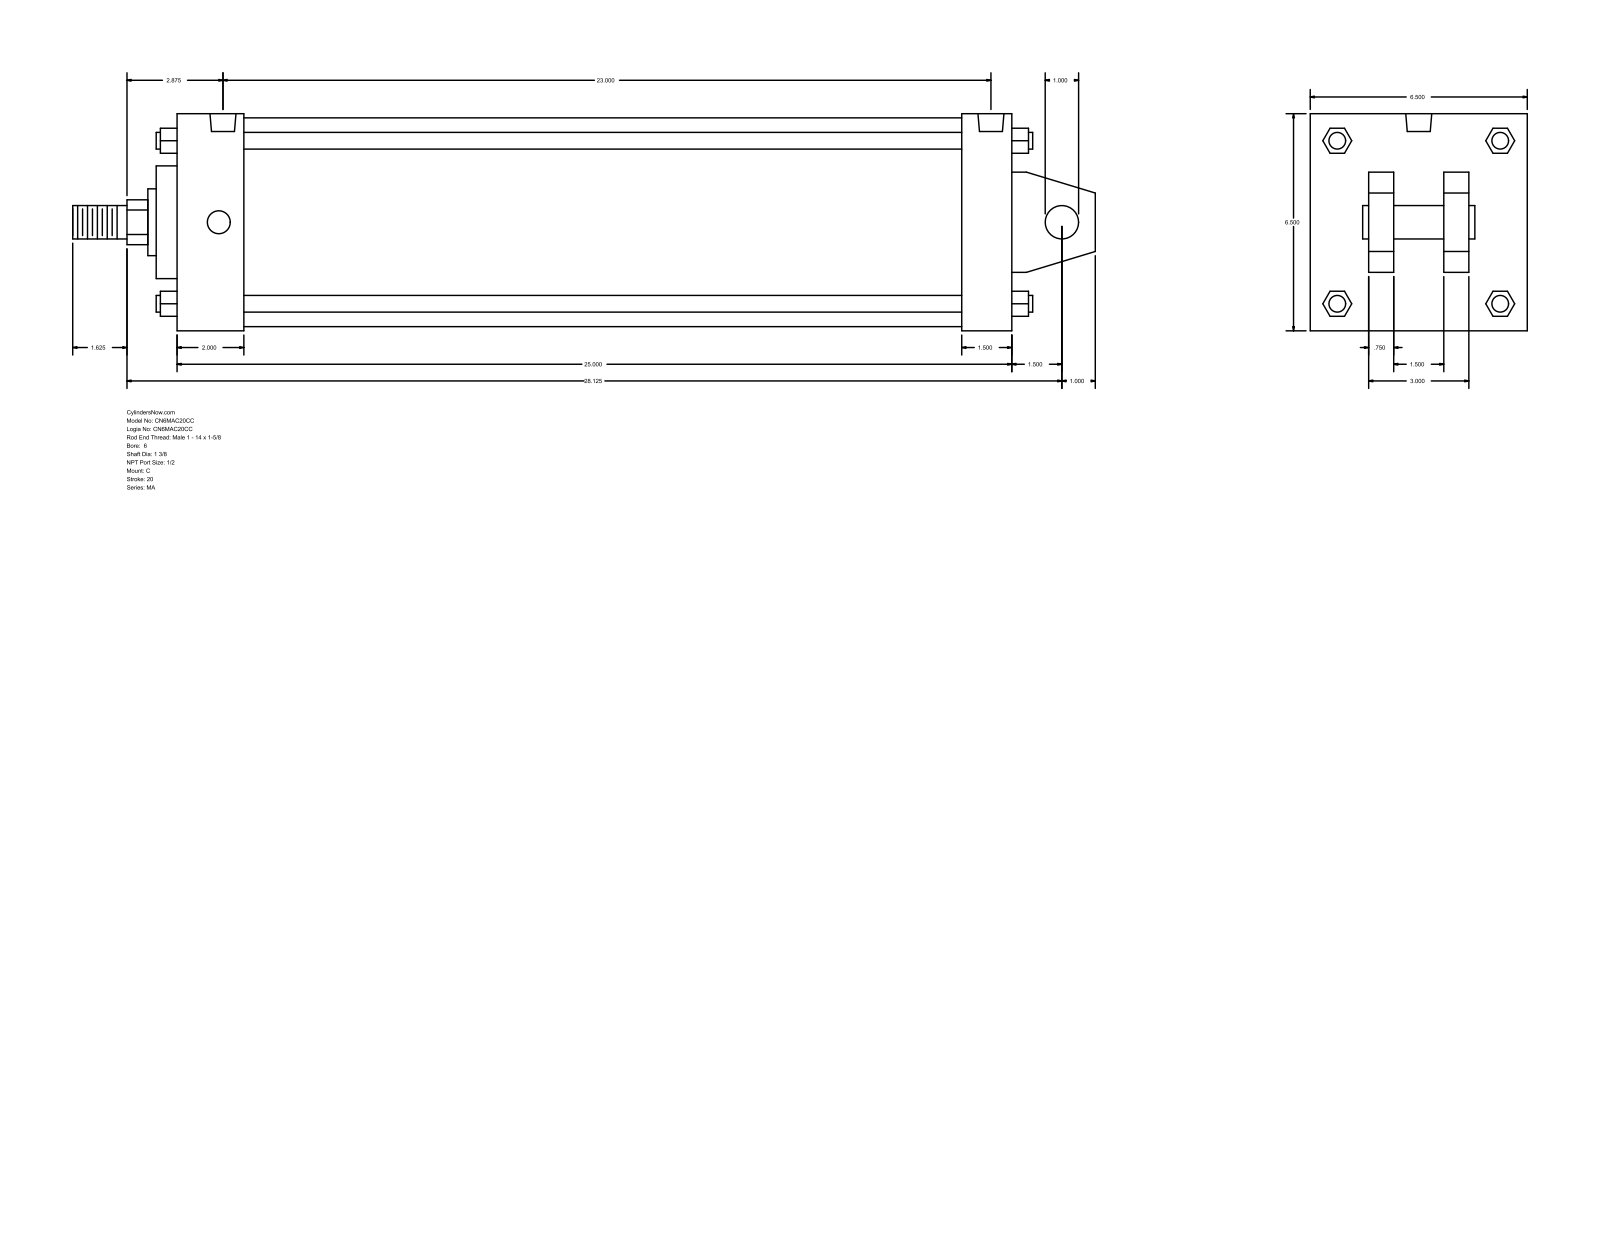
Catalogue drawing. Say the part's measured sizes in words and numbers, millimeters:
The part is named "MA_C__0600_1.375". Its 3-D file was written by "GSSL Pune (CONFIG_CONTROL_DESIGN)". It is 0 solids with 141 faces: 109 planar, 32 cylindrical and 0 other. Overall it measures 777.88 by 165.1 by 165.1 millimeters. Round holes: 4 of diameter 17.46, 2 of diameter 19.77. Round bosses or shafts: 4 of diameter 12.7, 2 of diameter 25.4, 1 of diameter 158.75, 1 of diameter 85.72, 1 of diameter 50.8, 1 of diameter 34.92. Partial cylindrical surfaces (rounded edges, fillets, slot ends): 1 of radius 17.06. The main face-to-face distances are 165.1, 635, 38.1, 19.05, 63.5, 101.6, 50.8, 44.45, 120.65, 596.9. The hole center spacings are 584.2, 3.18, 581.02, 587.38.
